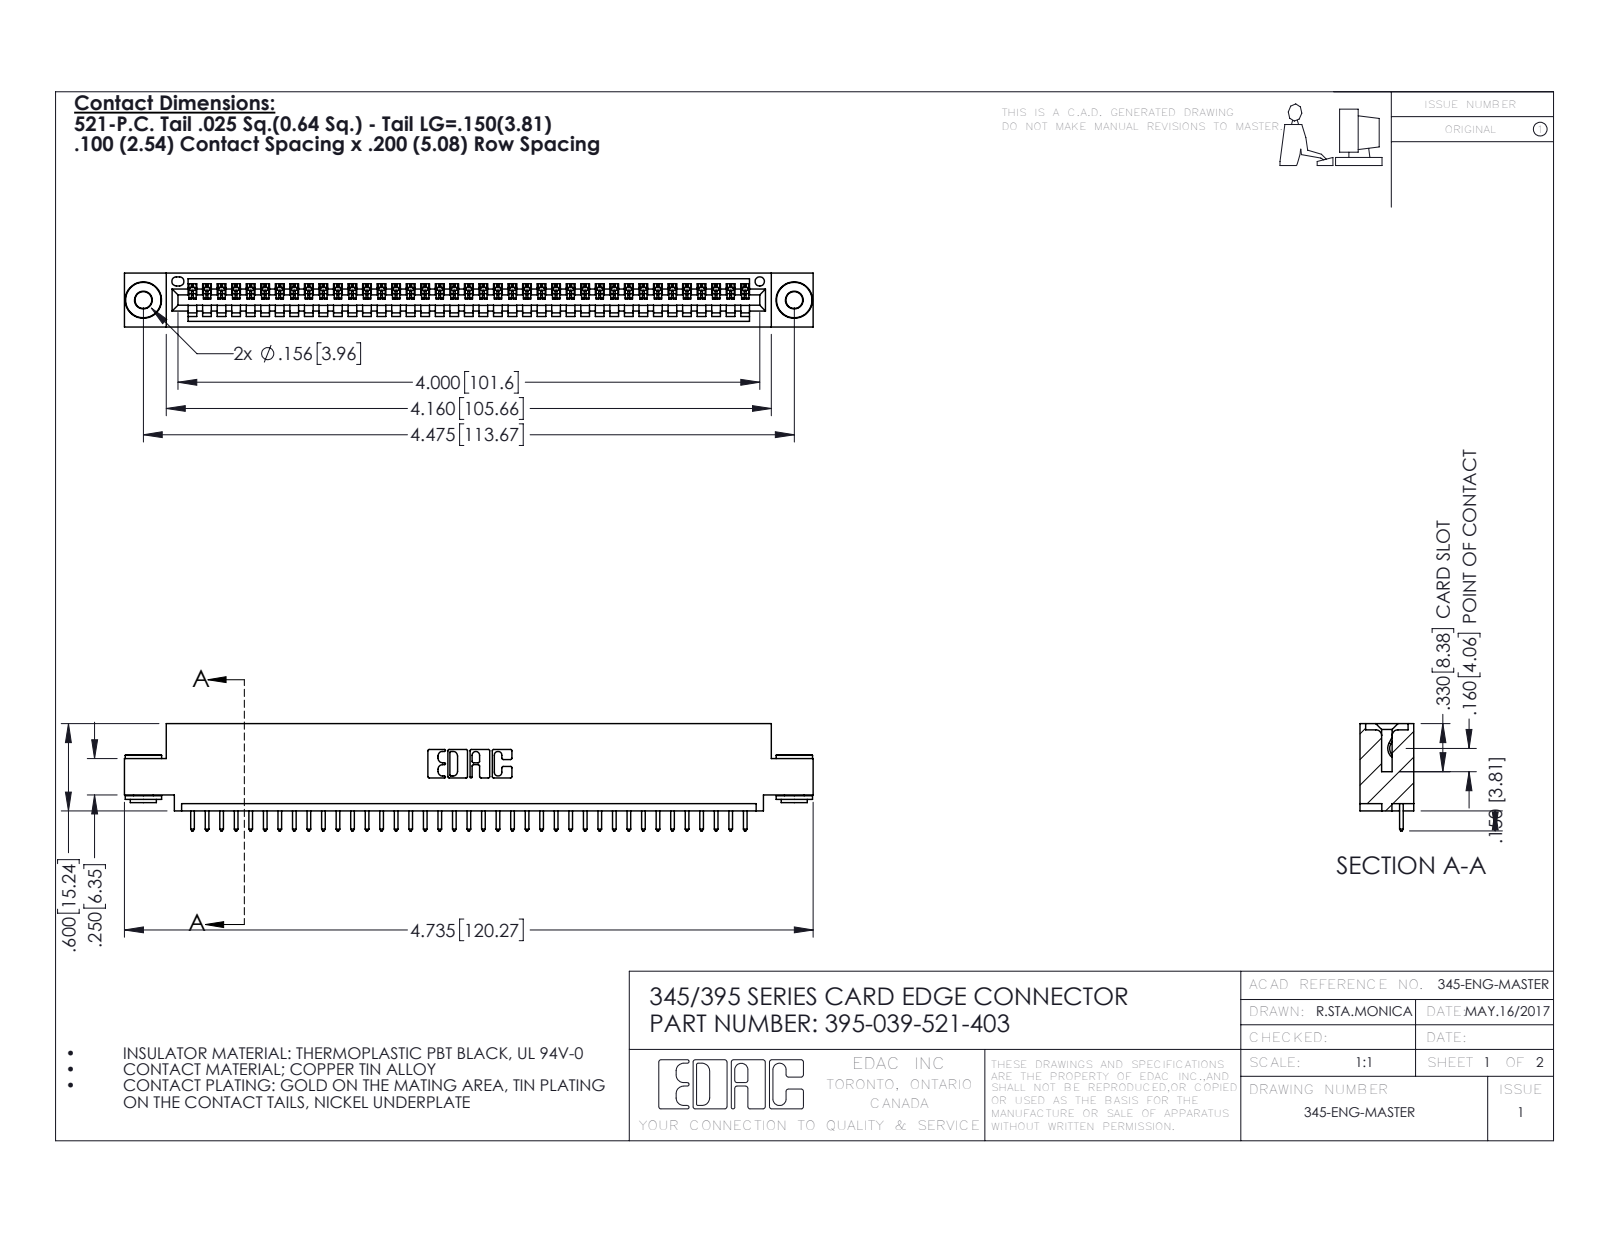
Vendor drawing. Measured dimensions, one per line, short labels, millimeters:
name: 395-039-521-403; 345-250-002_345-250-002-102; 345-292-001_345-293-121; 345 Part_0.110 Offset - 0.156 Dia-TH
written by: SolidWorks 2016 (CONFIG_CONTROL_DESIGN)
unit: mm
bodies: 42 solids, 2430 faces (1654 planar, 768 cylindrical, 8 other)
size: 120.3 × 18.7 × 9.4
volume: 11 200 mm³; area: 14 750 mm²
holes: 2× ⌀2.9, 2× ⌀4, 1× ⌀1.6
bosses: 2× ⌀6.4, 2× ⌀4.6, 2× ⌀3.5
rounds: 78× R0.2, 78× R0.3, 22× R0.3, 6× R0.2, 6× R0.8, 3× R0.7, 2× R0.8, 2× R1
face distances: 1.8, 7.6, 9.4, 5.1, 0.6, 2.5, 6.9, 5.7, 3.8, 1.8
hole spacings: 6.9, 107.7, 113.7
